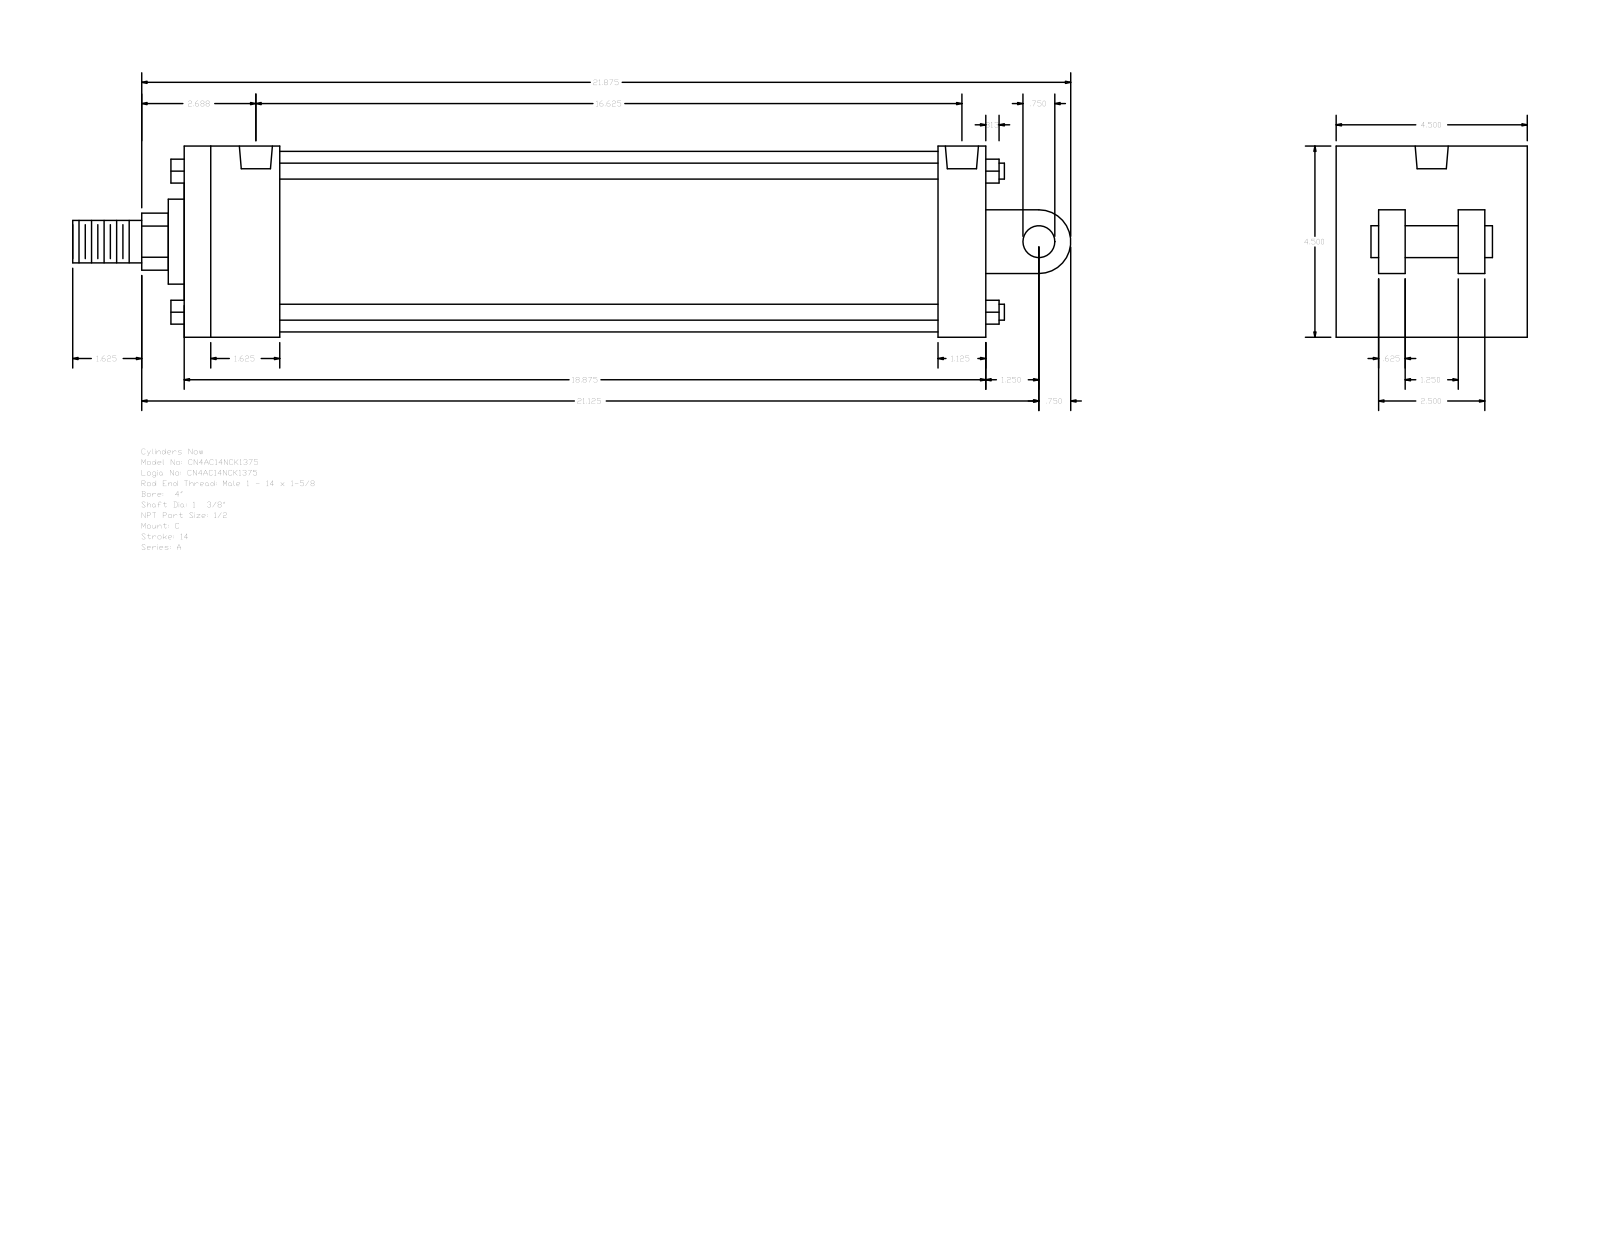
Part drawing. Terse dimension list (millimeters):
name: A_C__0400_1.375
written by: GSSL Pune (CONFIG_CONTROL_DESIGN)
unit: mm
bodies: 0 solids, 135 faces (102 planar, 33 cylindrical, 0 other)
size: 596.9 × 114.3 × 114.3
holes: 4× ⌀8.73, 2× ⌀19.77
bosses: 4× ⌀9.53, 1× ⌀107.95, 1× ⌀50.8, 1× ⌀34.92, 1× ⌀25.4, 1× ⌀19.05
rounds: 1× R17.06, 1× R19.05
face distances: 114.3, 479.42, 57.15, 73.03, 450.85, 28.57, 393.7, 422.27, 41.27, 25.4
hole spacings: 3.18, 415.92, 419.1, 422.28
